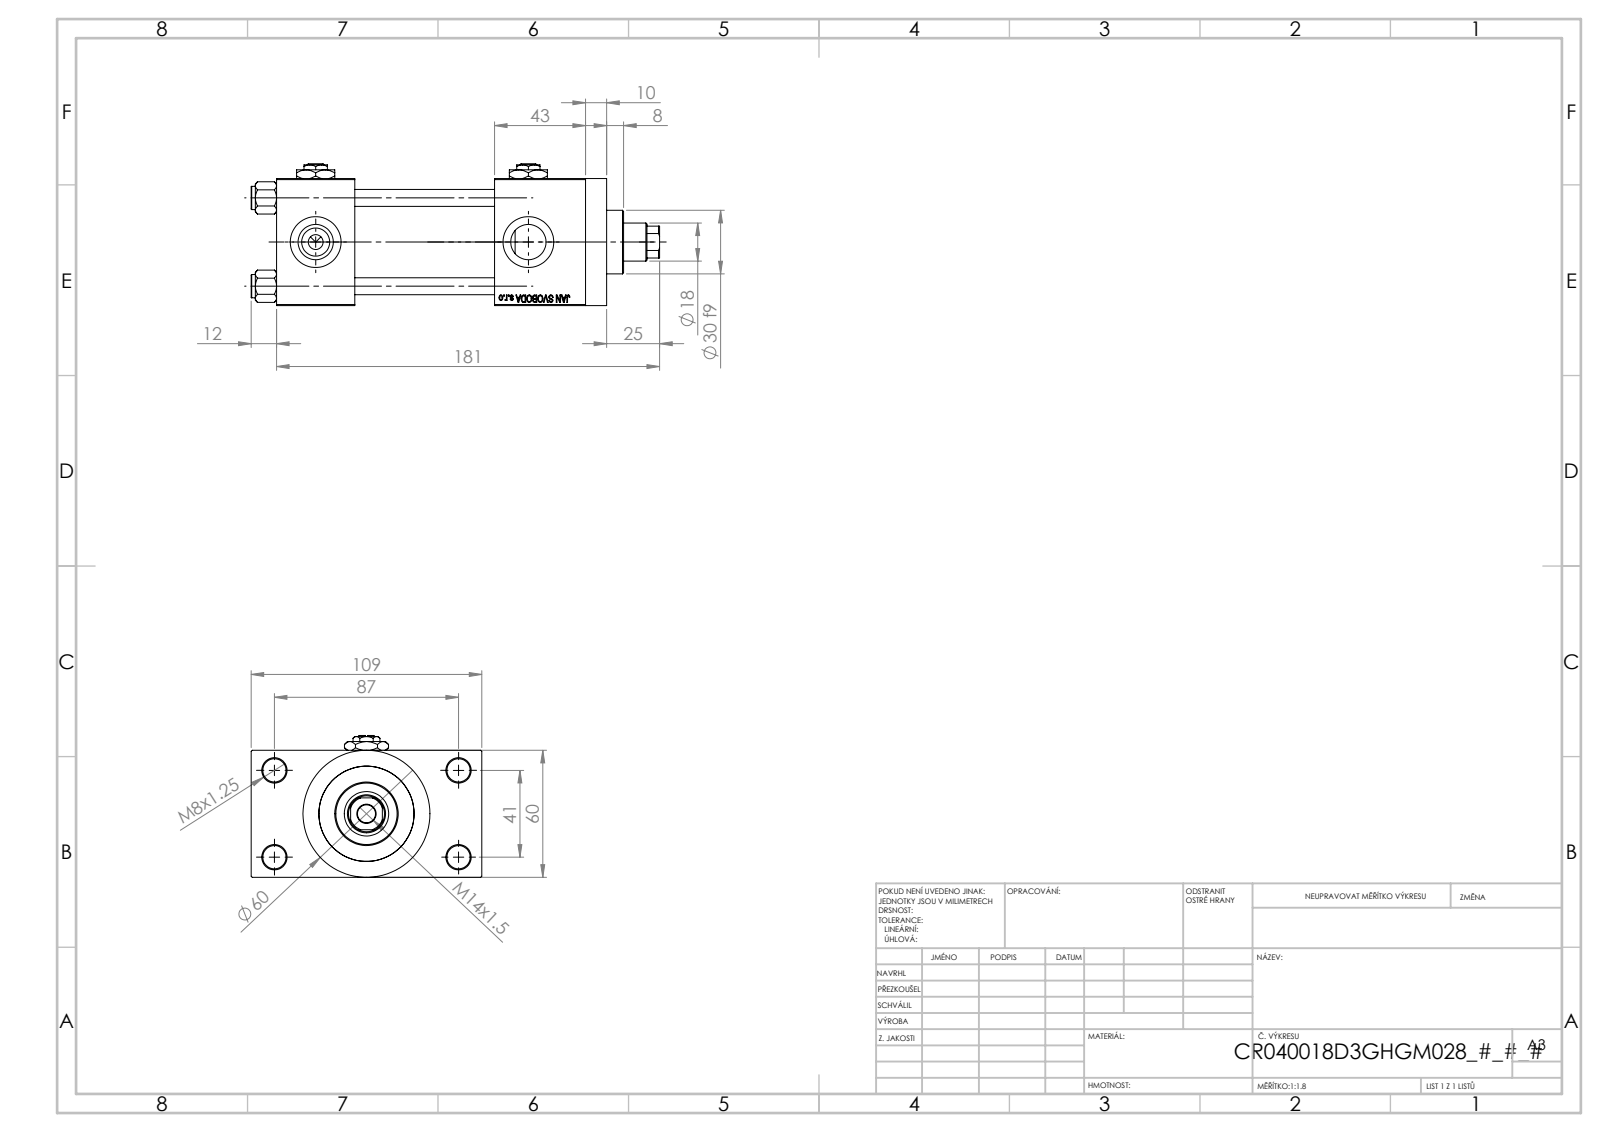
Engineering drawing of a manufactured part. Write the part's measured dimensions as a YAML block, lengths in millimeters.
part_name: "NUT_M5_D; V215CR_D_Body; V215_VC_A; Zatka_pro_OIL_PORT (+2 more)"
step_written_by: "SolidWorks 2019 (CONFIG_CONTROL_DESIGN)"
units: millimeters
bodies: {solids: 13, faces: 1205, planar: 546, cylindrical: 99, other: 560}
overall_size: [193, 109, 67]
volume: 517223
surface_area: 128610
round_holes:
  - {diameter: 8, count: 4}
  - {diameter: 11, count: 4}
  - {diameter: 16.66, count: 4}
  - {diameter: 24, count: 4}
  - {diameter: 7, count: 3}
  - {diameter: 8.5, count: 1}
  - {diameter: 18, count: 1}
  - {diameter: 21, count: 1}
  - {diameter: 31, count: 1}
  - {diameter: 40, count: 1}
  - {diameter: 45, count: 1}
round_bosses_or_shafts:
  - {diameter: 11, count: 4}
  - {diameter: 60, count: 1}
  - {diameter: 46, count: 1}
  - {diameter: 30, count: 1}
partial_cylinders:
  - {radius: 8.5, count: 1}
face_to_face_distances: [60, 109, 66, 24.5, 84.5, 37, 103, 43, 146, 10]
hole_center_spacings: [22.65, 29.49, 41.7, 47.15, 48.09, 64.35, 76.49, 41]
